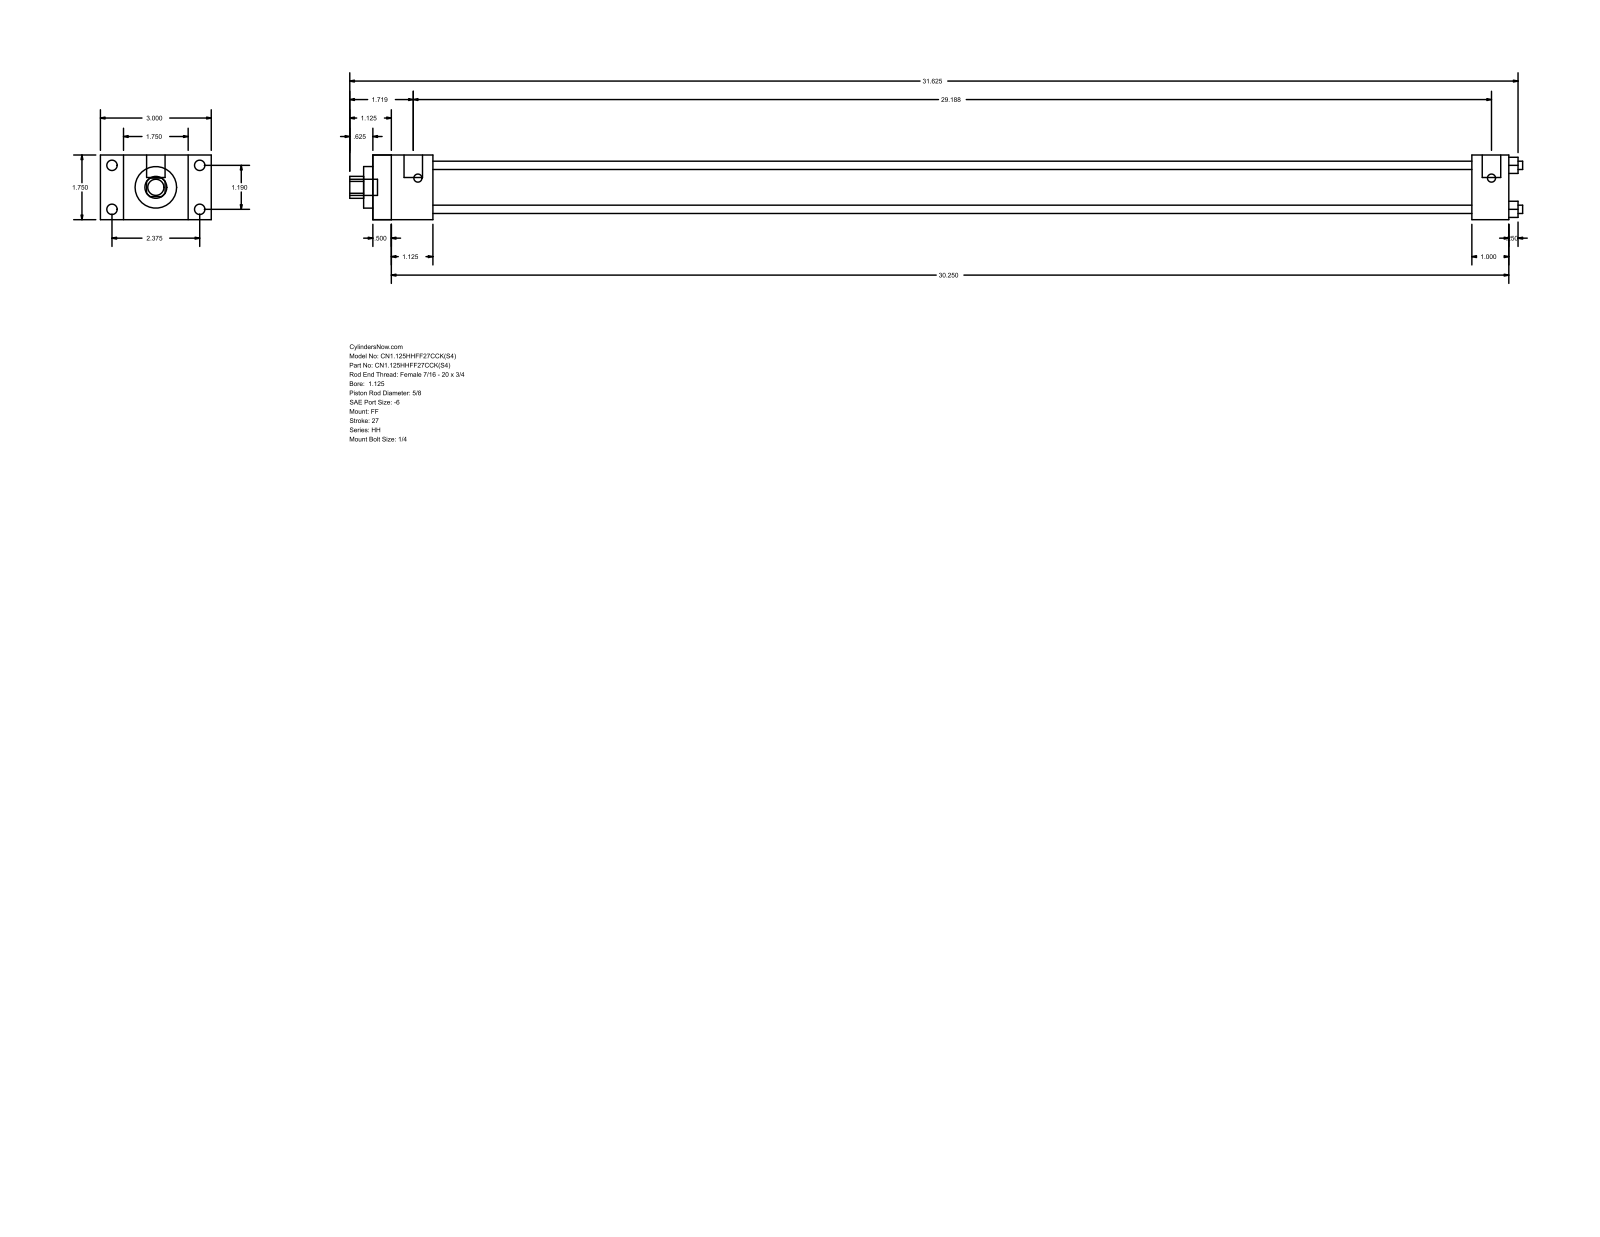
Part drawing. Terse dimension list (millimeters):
name: HH_FF__0112_0.625
written by: GSSL Pune (CONFIG_CONTROL_DESIGN)
unit: mm
bodies: 0 solids, 92 faces (64 planar, 28 cylindrical, 0 other)
size: 806.45 × 76.2 × 44.45
holes: 4× ⌀5.71, 1× ⌀15.88, 1× ⌀28.57, 1× ⌀34.92
bosses: 4× ⌀7.14, 4× ⌀5.56, 2× ⌀12.7, 1× ⌀11.11
rounds: 1× R7.54
face distances: 44.46, 781.04, 12.69, 768.35, 15.87, 60.33, 28.58, 41.27, 755.64, 742.95
hole spacings: 21.37, 30.22, 42.74
